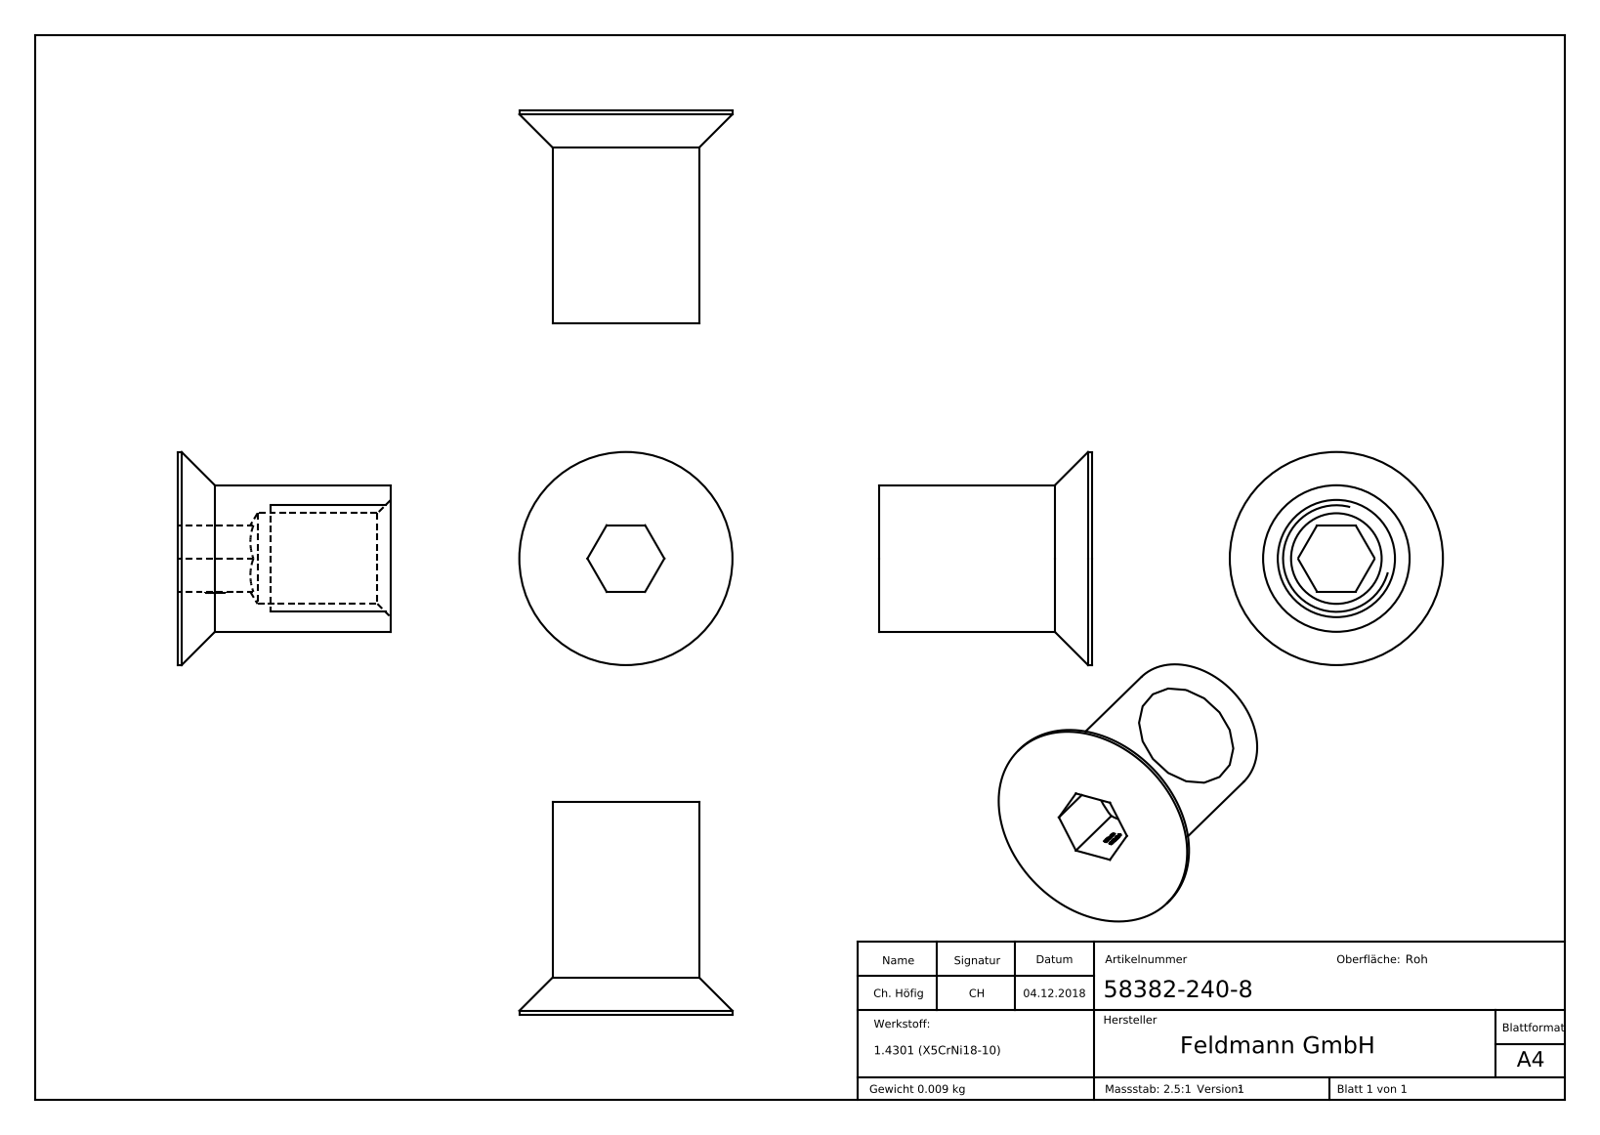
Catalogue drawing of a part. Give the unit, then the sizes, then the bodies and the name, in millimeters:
Units: millimetres
Overall size (bounding box): 16 × 16 × 16
Round holes (diameter × count): ⌀6.8 ×1
Round bosses / shafts (diameter × count): ⌀16 ×1, ⌀11 ×1
Main face-to-face distances: 5, 16, 5.1, 0.45, 0.68, 0.47, 0.55, 0.5, 0.49, 0.51
Volume: 1 169 mm³ · Surface area: 1 176 mm²
Bodies: 1 solid, 288 faces (134 planar, 6 cylindrical, 148 other)
Part name (STEP PRODUCT): 58382-240-8
STEP written by: SolidWorks 2015 (CONFIG_CONTROL_DESIGN)
